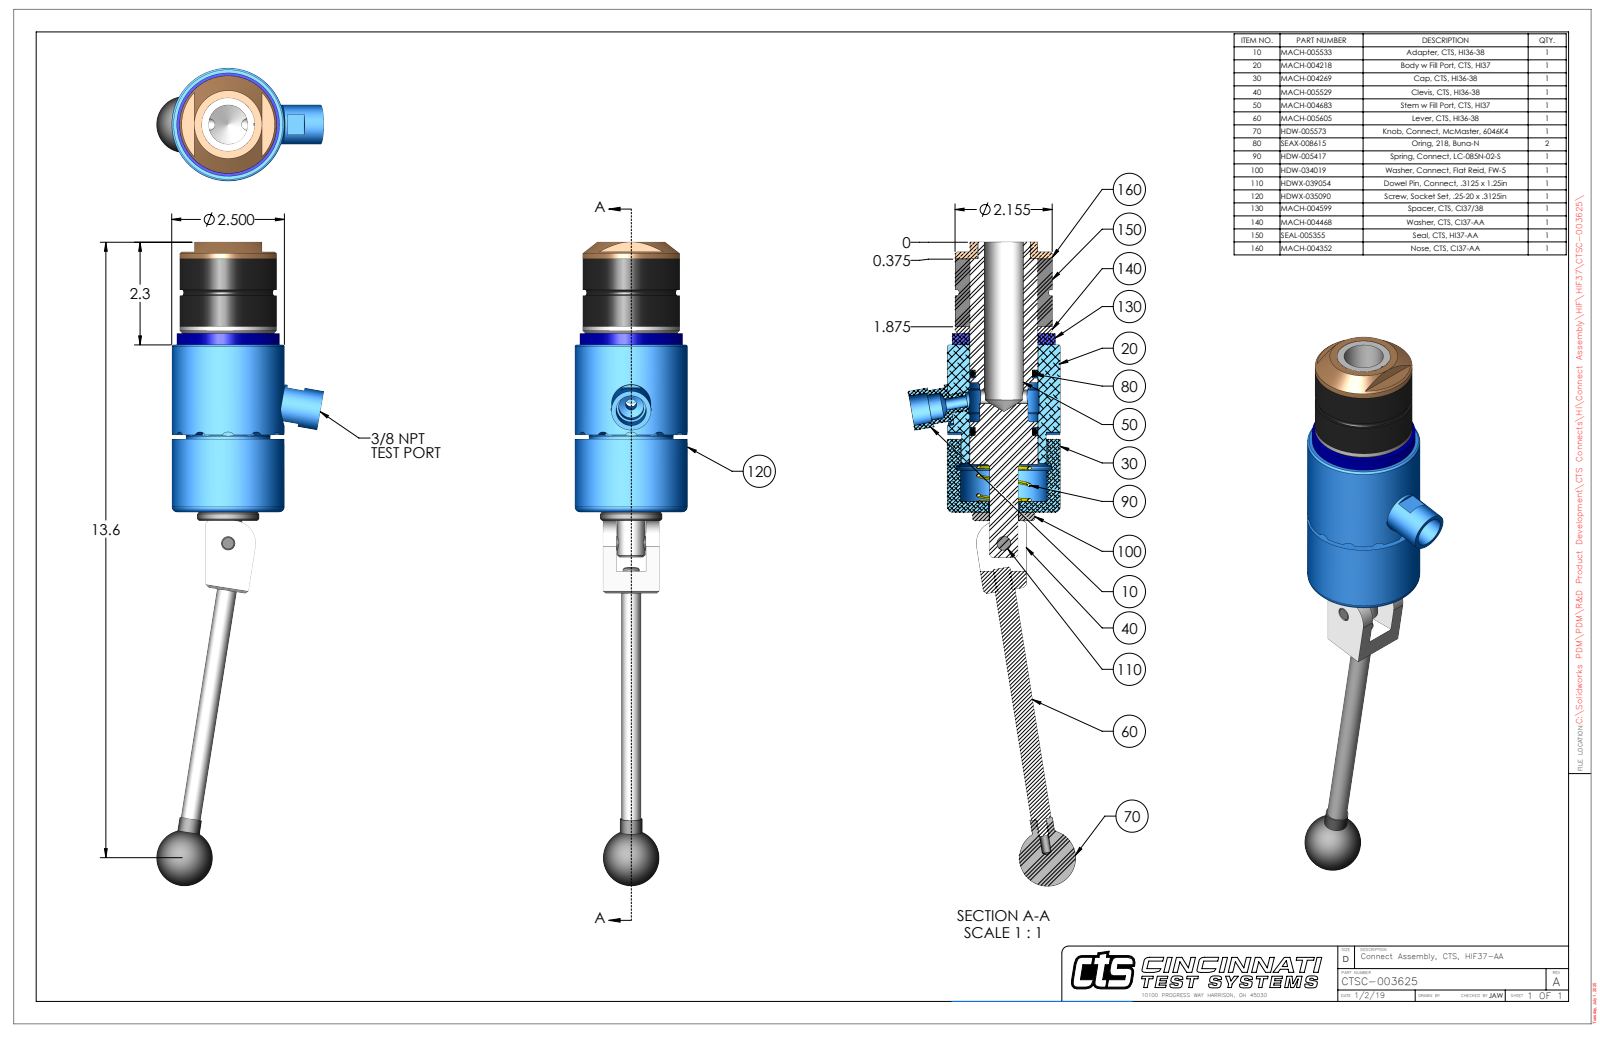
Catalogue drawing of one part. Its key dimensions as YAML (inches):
part_name: "CTSC-003625"
step_written_by: "SolidWorks 2023 (AUTOMOTIVE_DESIGN)"
units: inches
bodies: {solids: 10, faces: 382, planar: 168, cylindrical: 129, other: 85}
overall_size: [14.275, 3.716, 2.5]
volume: 27.69
surface_area: 143.6
round_holes:
  - {diameter: 0.201, count: 2}
  - {diameter: 0.15, count: 1}
  - {diameter: 0.25, count: 1}
  - {diameter: 0.311, count: 1}
  - {diameter: 0.312, count: 1}
  - {diameter: 0.313, count: 1}
  - {diameter: 0.314, count: 1}
  - {diameter: 0.562, count: 1}
  - {diameter: 0.656, count: 1}
  - {diameter: 0.696, count: 1}
  - {diameter: 0.875, count: 1}
  - {diameter: 1.172, count: 1}
round_bosses_or_shafts:
  - {diameter: 2.5, count: 1}
  - {diameter: 2.281, count: 1}
  - {diameter: 2.155, count: 1}
  - {diameter: 2.155, count: 1}
  - {diameter: 1.875, count: 1}
  - {diameter: 1.5, count: 1}
  - {diameter: 1.496, count: 1}
  - {diameter: 1.38, count: 1}
partial_cylinders:
  - {radius: 0.12, count: 12}
  - {radius: 0.029, count: 2}
  - {radius: 0.19, count: 1}
  - {radius: 0.195, count: 1}
  - {radius: 0.47, count: 1}
  - {radius: 0.473, count: 1}
  - {radius: 0.5, count: 1}
  - {radius: 1.175, count: 1}
face_to_face_distances: [1.902, 3.713, 5.615, 0.25, 1.5, 3.963, 1.652, 4.115, 0.402, 0.152]
hole_center_spacings: [0.74, 2.118, 2.858]
